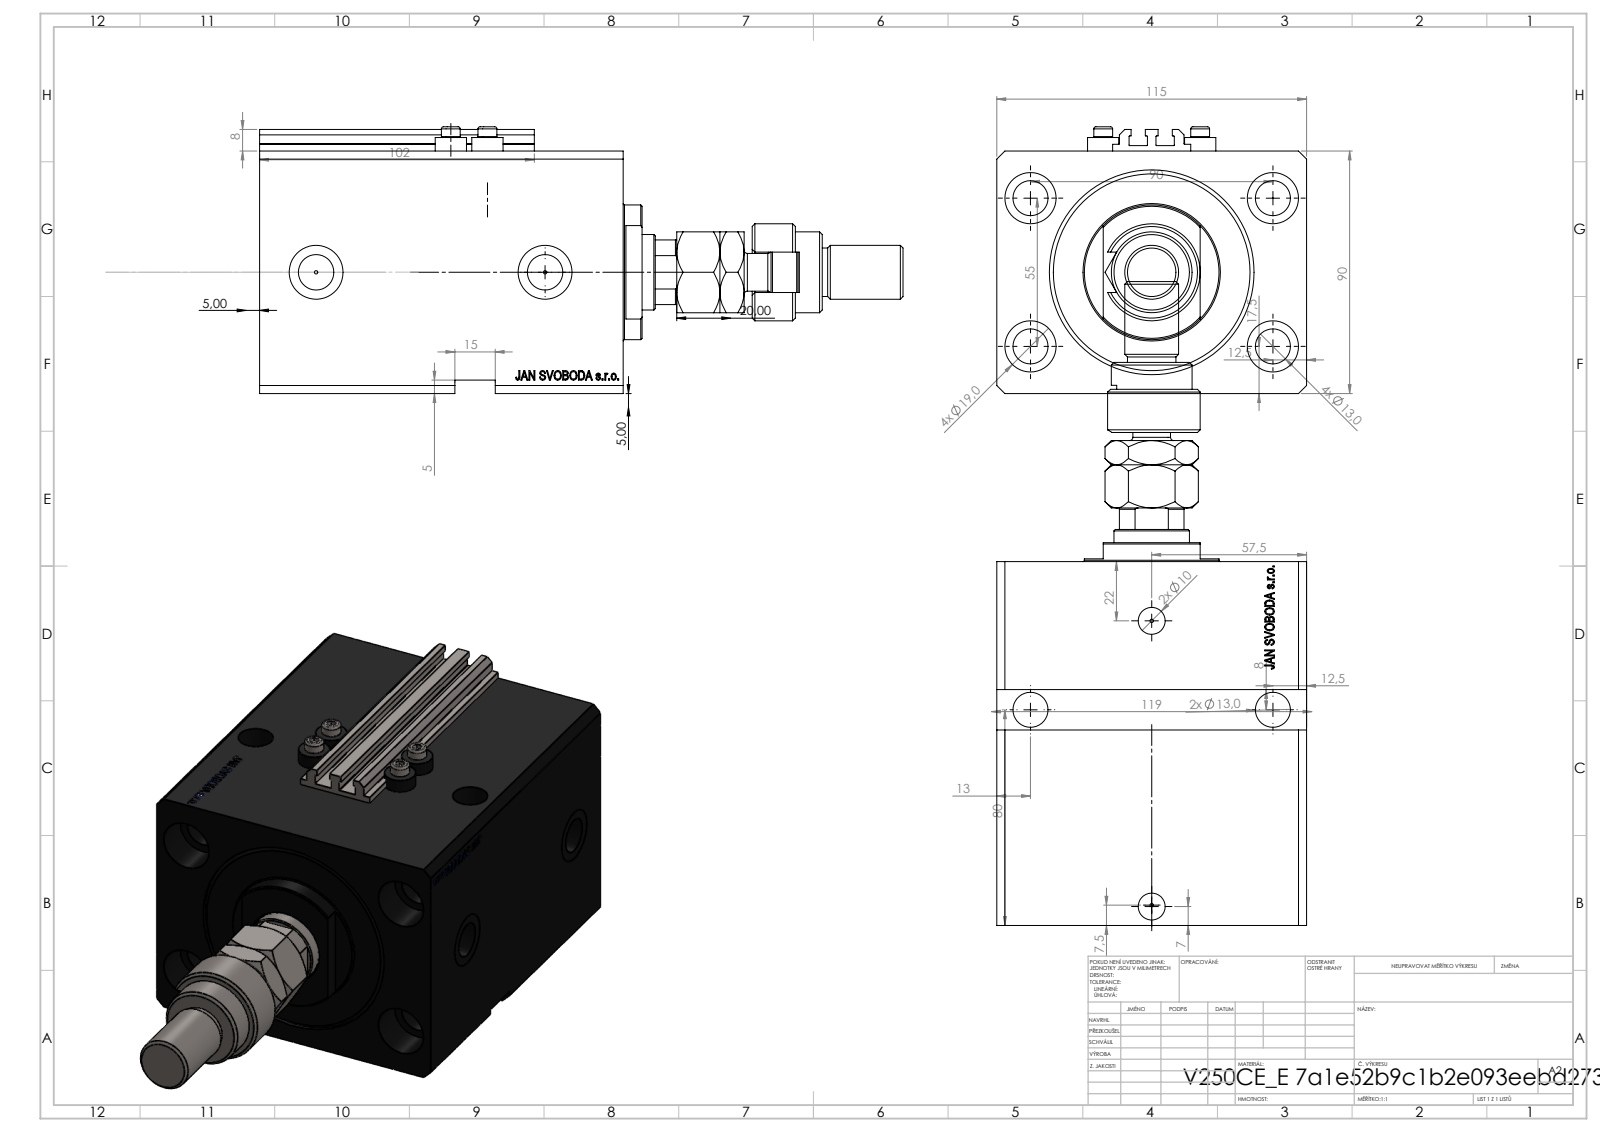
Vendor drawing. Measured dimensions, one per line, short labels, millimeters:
name: ALLEN BOLT V250CE; V250CE_E_Body; V250CE_C_VCP; MFA (+2 more)
written by: SolidWorks 2019 (CONFIG_CONTROL_DESIGN)
unit: mm
bodies: 10 solids, 1228 faces (575 planar, 171 cylindrical, 482 other)
size: 239 × 115 × 99
volume: 1 205 000 mm³; area: 201 083 mm²
holes: 8× ⌀13, 4× ⌀1.25, 4× ⌀4, 4× ⌀19, 2× ⌀10, 2× ⌀13.16, 2× ⌀20, 1× ⌀18.5, 1× ⌀28, 1× ⌀63, 1× ⌀76
bosses: 4× ⌀11.6, 4× ⌀7, 1× ⌀50, 1× ⌀36, 1× ⌀30, 1× ⌀22, 1× ⌀20, 1× ⌀18
rounds: 10× R0.2, 1× R7.5, 1× R12, 1× R13.5
face distances: 115, 90, 20, 135, 17.9, 117.1, 97.1, 65, 13, 30
hole spacings: 52.74, 55.8, 85.76, 90, 13.6, 27.39, 28.46, 33.62
